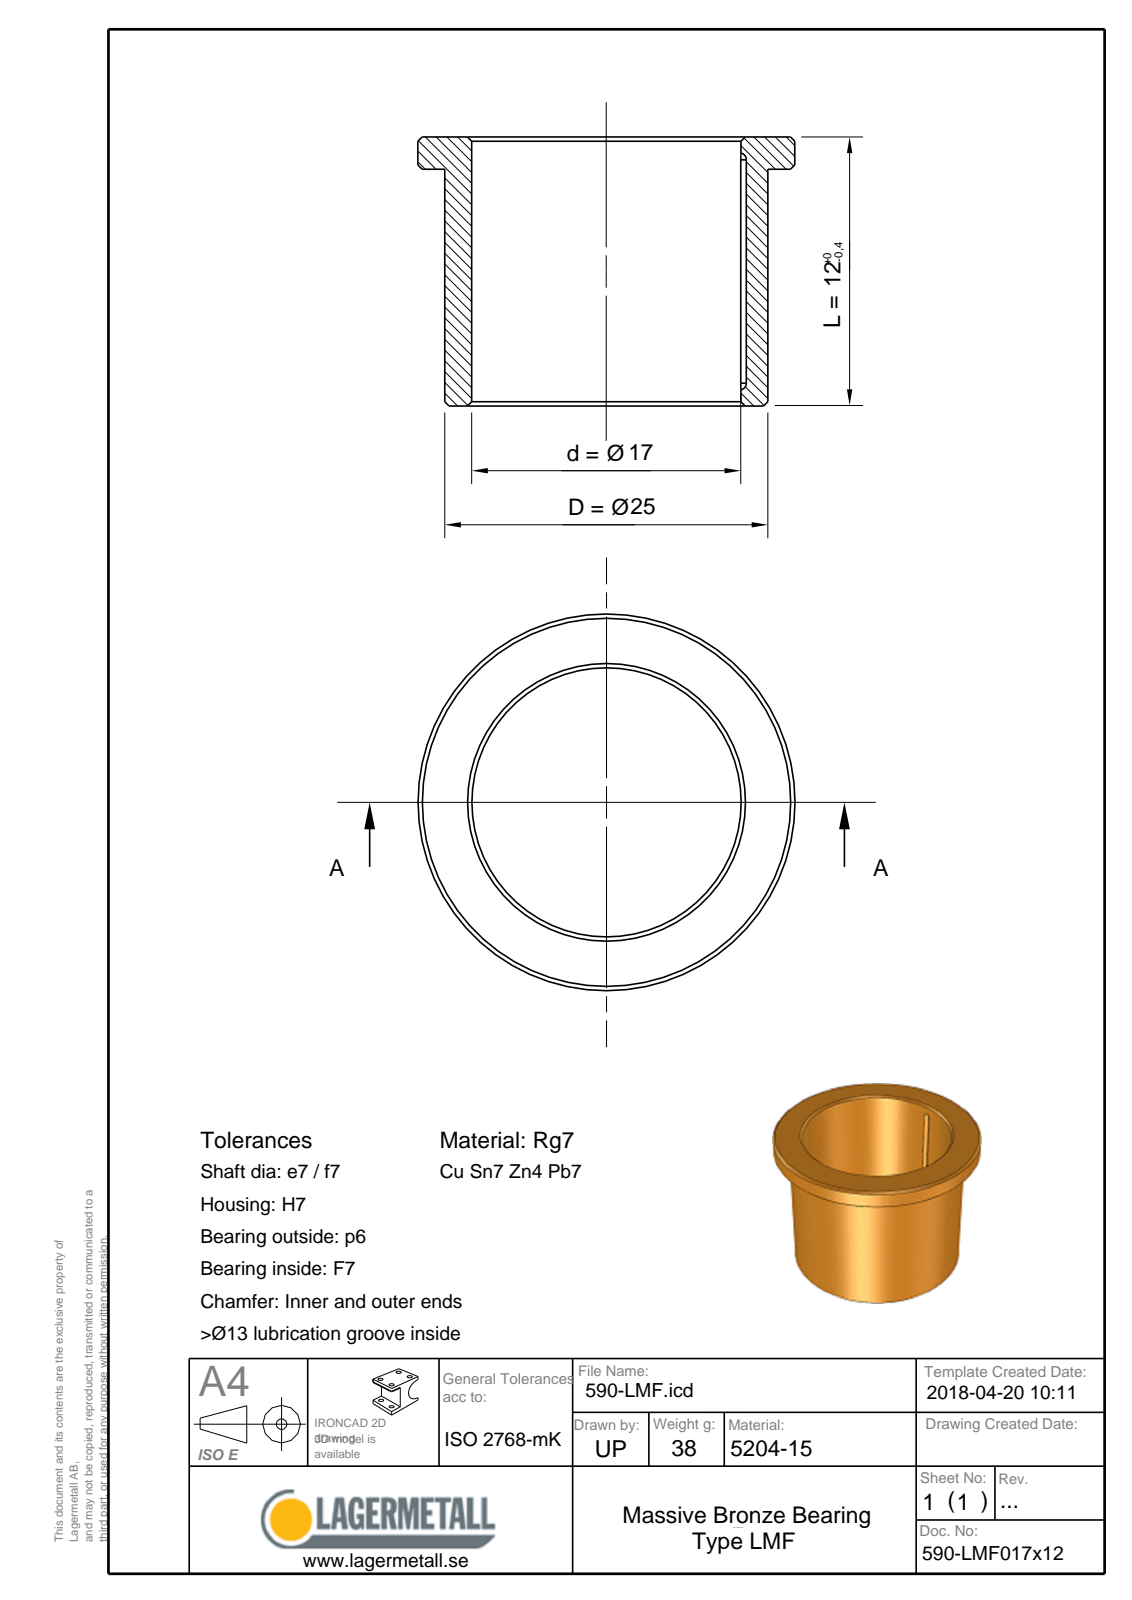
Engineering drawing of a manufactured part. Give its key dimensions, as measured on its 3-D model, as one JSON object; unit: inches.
{"part_name": "590-LMF017x12", "step_written_by": "Spatial InterOp 3D (CONFIG_CONTROL_DESIGN)", "units": "inches", "bodies": {"solids": 1, "faces": 18, "planar": 5, "cylindrical": 6, "other": 7}, "overall_size": [1.26, 1.26, 0.472], "volume_in3": 0.266, "surface_area_in2": 4.219, "round_holes": [[0.669, 1]], "round_bosses_or_shafts": [[1.26, 1], [0.984, 1]], "partial_cylinders_radius": [[0.03, 3]], "face_to_face_distances": [0.157, 0.315, 0.472, 0.059]}
